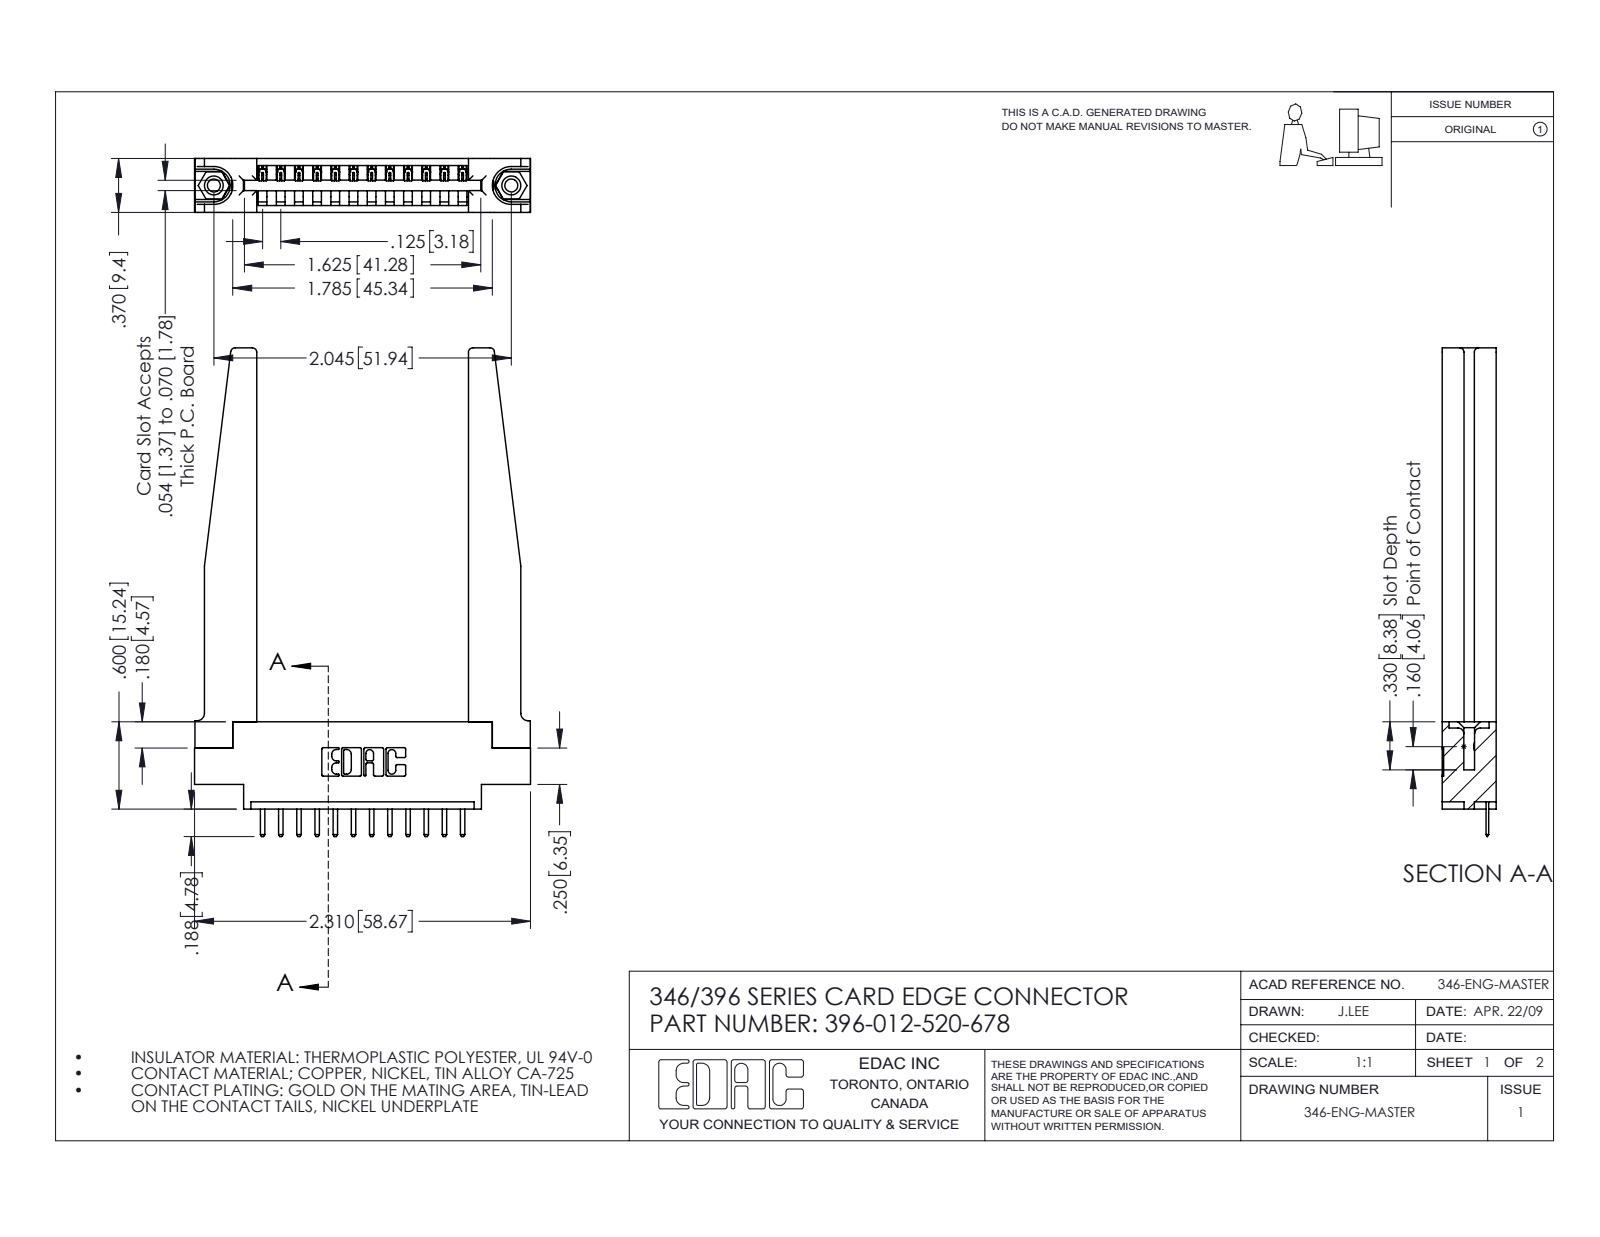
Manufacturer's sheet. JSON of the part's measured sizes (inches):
{"part_name": "346 Part_0.170 Offset - 0.156 Dia-TH; 345-250-001_345-250-001-102; 396-012-520-678; 345-292-001_345-293-120 (+1 more)", "step_written_by": "SolidWorks 2016 (CONFIG_CONTROL_DESIGN)", "units": "inches", "bodies": {"solids": 17, "faces": 1104, "planar": 726, "cylindrical": 326, "other": 52}, "overall_size": [3.358, 2.31, 0.37], "volume_in3": 0.74, "surface_area_in2": 19.82, "round_holes": [[0.089, 2], [0.125, 2], [0.156, 2], [0.064, 1]], "round_bosses_or_shafts": [[0.155, 2]], "partial_cylinders_radius": [[0.01, 26], [0.006, 24], [0.01, 22], [0.03, 8], [0.007, 6], [0.031, 6], [0.026, 3], [0.031, 2]], "face_to_face_distances": [0.37, 0.15, 0.072, 0.148, 0.048, 0.322, 0.22, 0.102, 0.173, 0.25], "hole_center_spacings": [0.246, 1.839, 2.045]}
